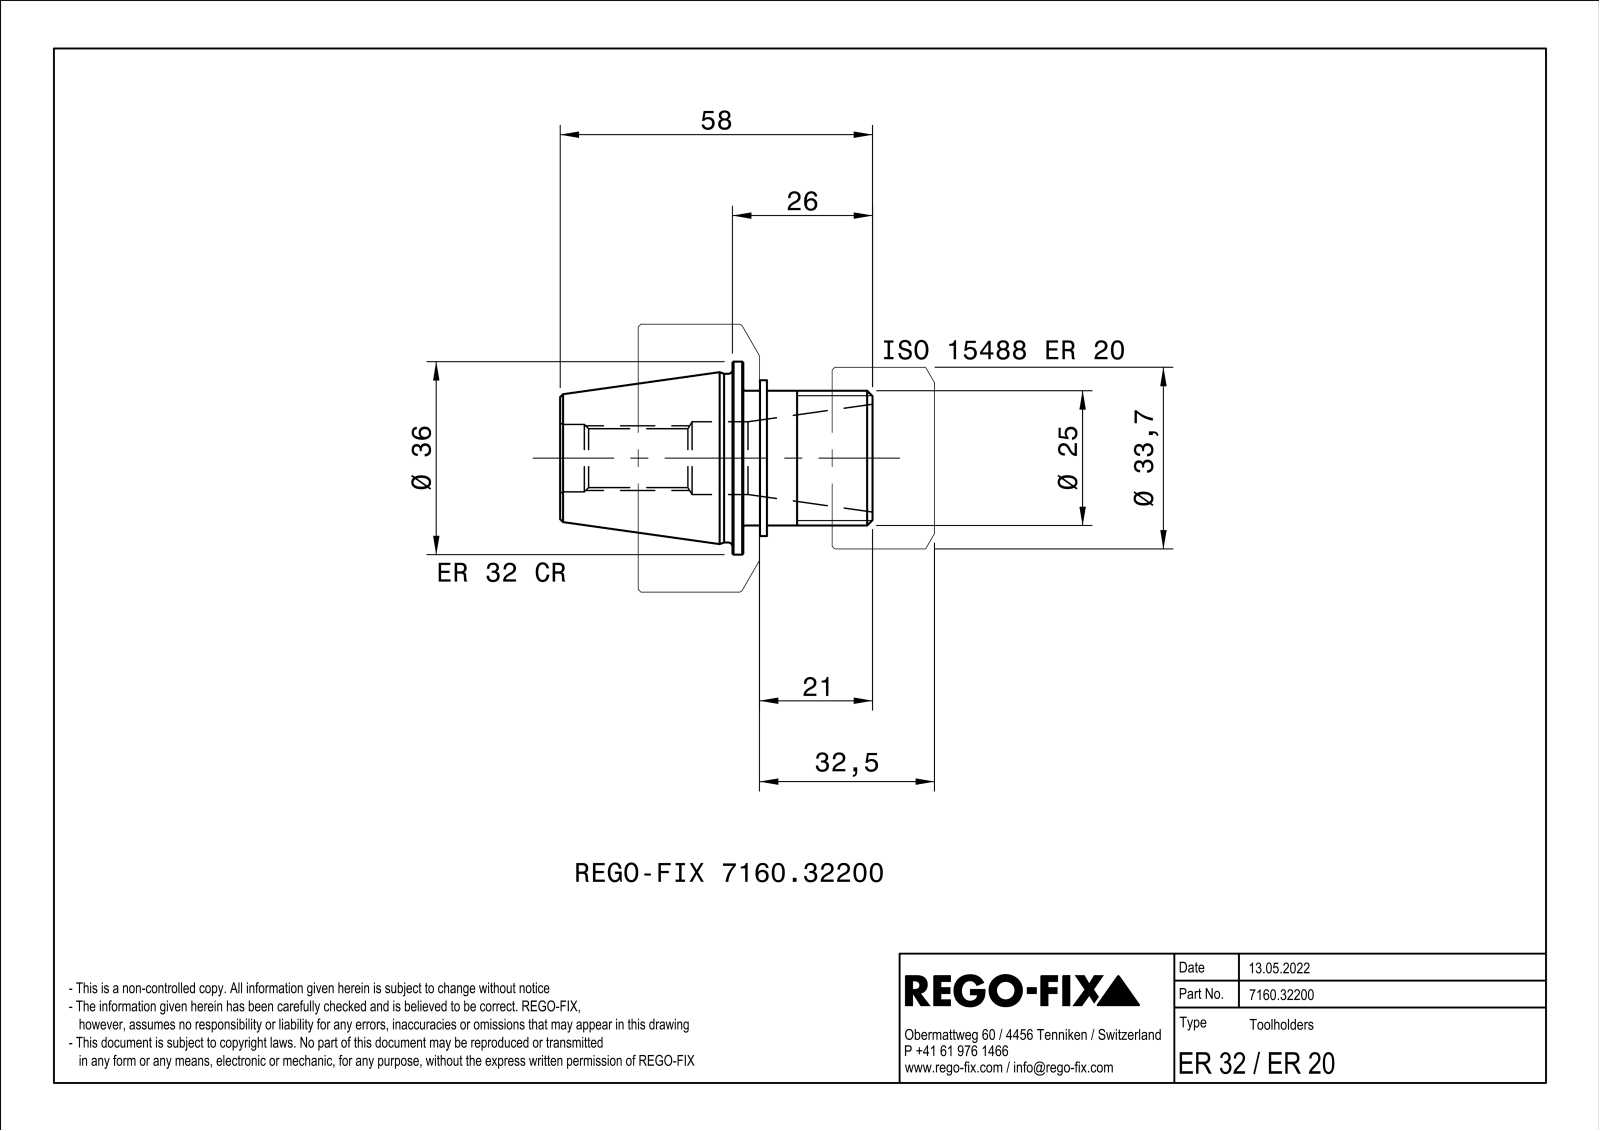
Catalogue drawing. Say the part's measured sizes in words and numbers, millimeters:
The part is named "NOCUT". Its 3-D file was written by "SIEMENS PLM Software Solid Edge ST10 (AUTOMOTIVE_DESIGN)". It is 1 solid with 105 faces: 55 planar, 13 cylindrical and 37 other. Overall it measures 58 by 49.7 by 49.7 millimeters. Its volume is 39 262 cubic millimeters and its surface area 16 320 square millimeters. Round holes: 1 of diameter 10.92, 1 of diameter 12.5, 1 of diameter 13.5, 1 of diameter 25.4, 1 of diameter 38.38, 1 of diameter 40.5. Round bosses or shafts: 1 of diameter 49.7, 1 of diameter 35.8, 1 of diameter 31.3, 1 of diameter 28.9, 1 of diameter 25, 1 of diameter 22.4. The main face-to-face distances are 17, 20, 1.3, 3, 37, 34, 4.3, 21.3, 38.3, 1.2.
